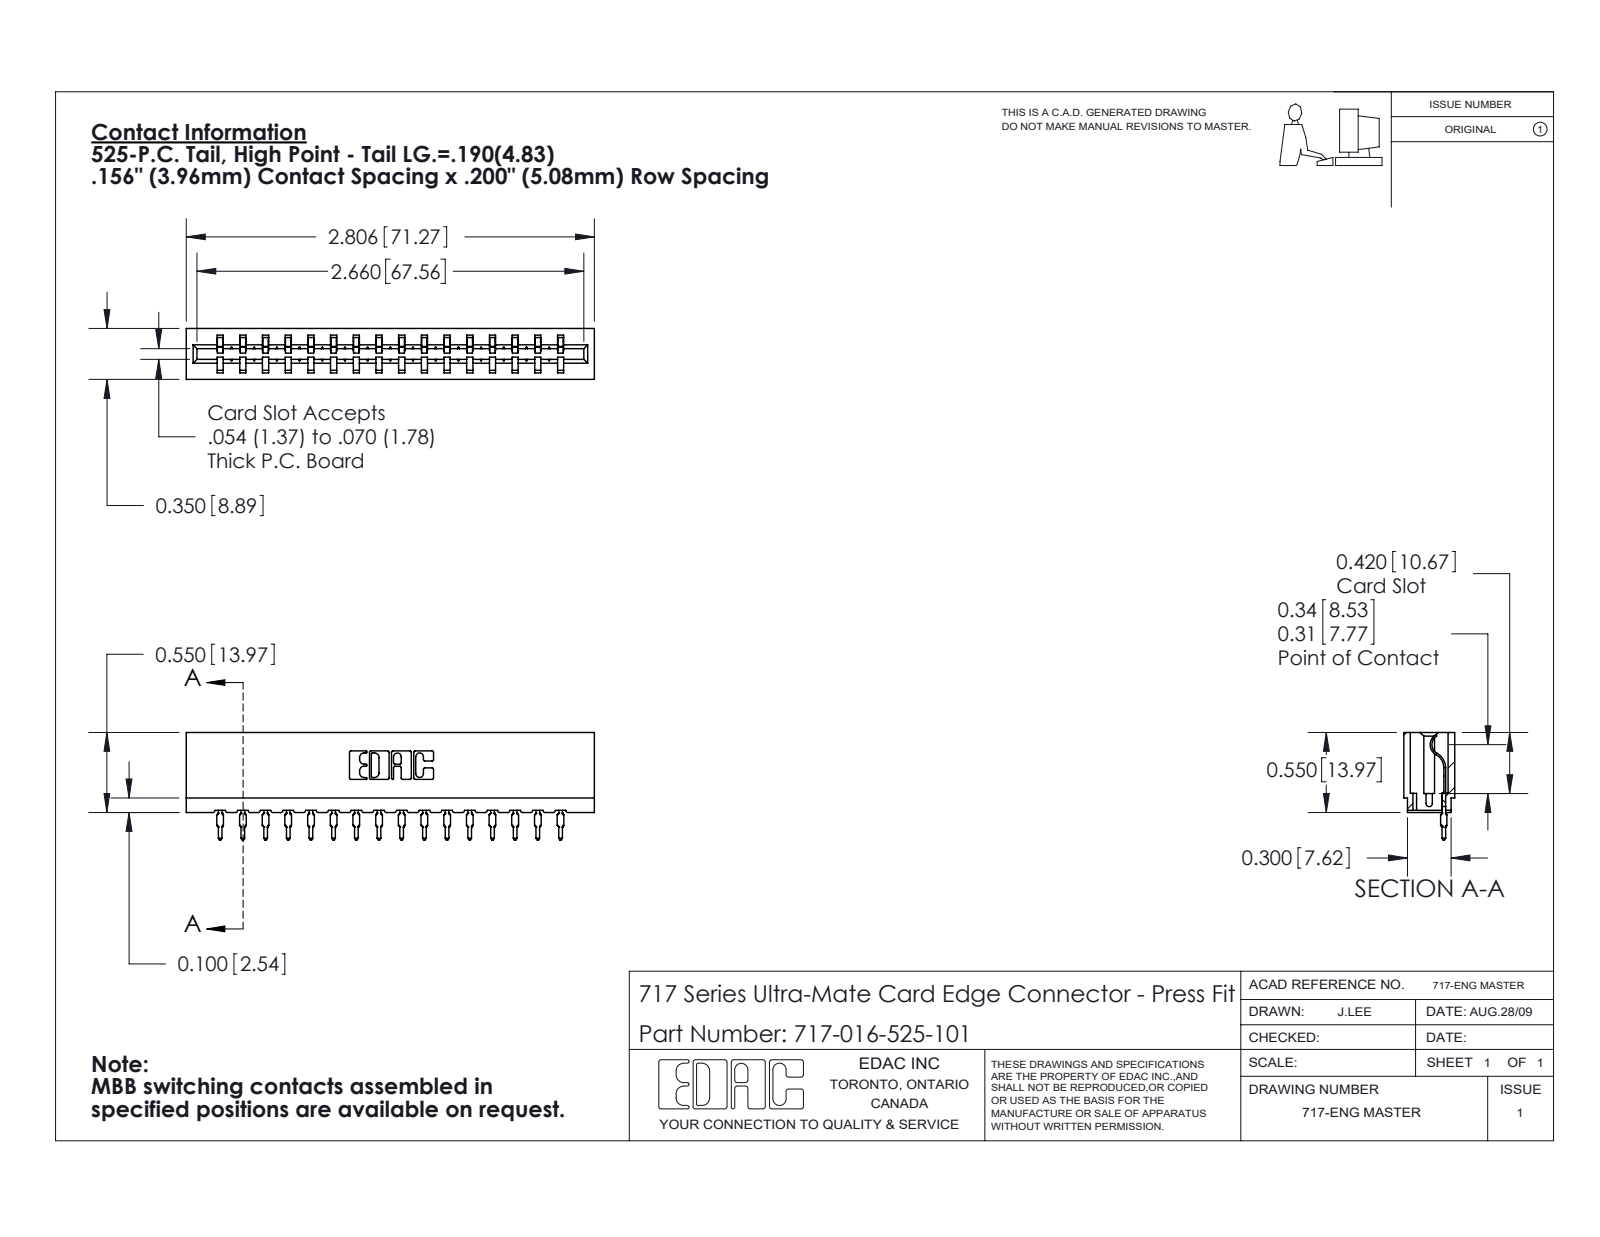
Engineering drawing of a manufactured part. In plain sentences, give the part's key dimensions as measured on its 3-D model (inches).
The part is named "717-016-525-101; 745-292-001_525; 717 Part_Insulator Option - 06". Its 3-D file was written by "SolidWorks 2020 (CONFIG_CONTROL_DESIGN)". It is 17 solids with 1902 faces: 1142 planar, 344 cylindrical and 416 other. Overall it measures 2.806 by 0.739 by 0.35 inches. Its volume is 0.374 cubic inches and its surface area 12.82 square inches. Partial cylindrical surfaces (rounded edges, fillets, slot ends): 32 of radius 0.015, 32 of radius 0.021, 22 of radius 0.01, 6 of radius 0.007, 6 of radius 0.031, 4 of radius 0.005, 4 of radius 0.011, 3 of radius 0.026. The main face-to-face distances are 0.212, 0.138, 0.35, 0.156, 0.468, 0.624, 0.198, 0.312, 0.074, 0.025.
